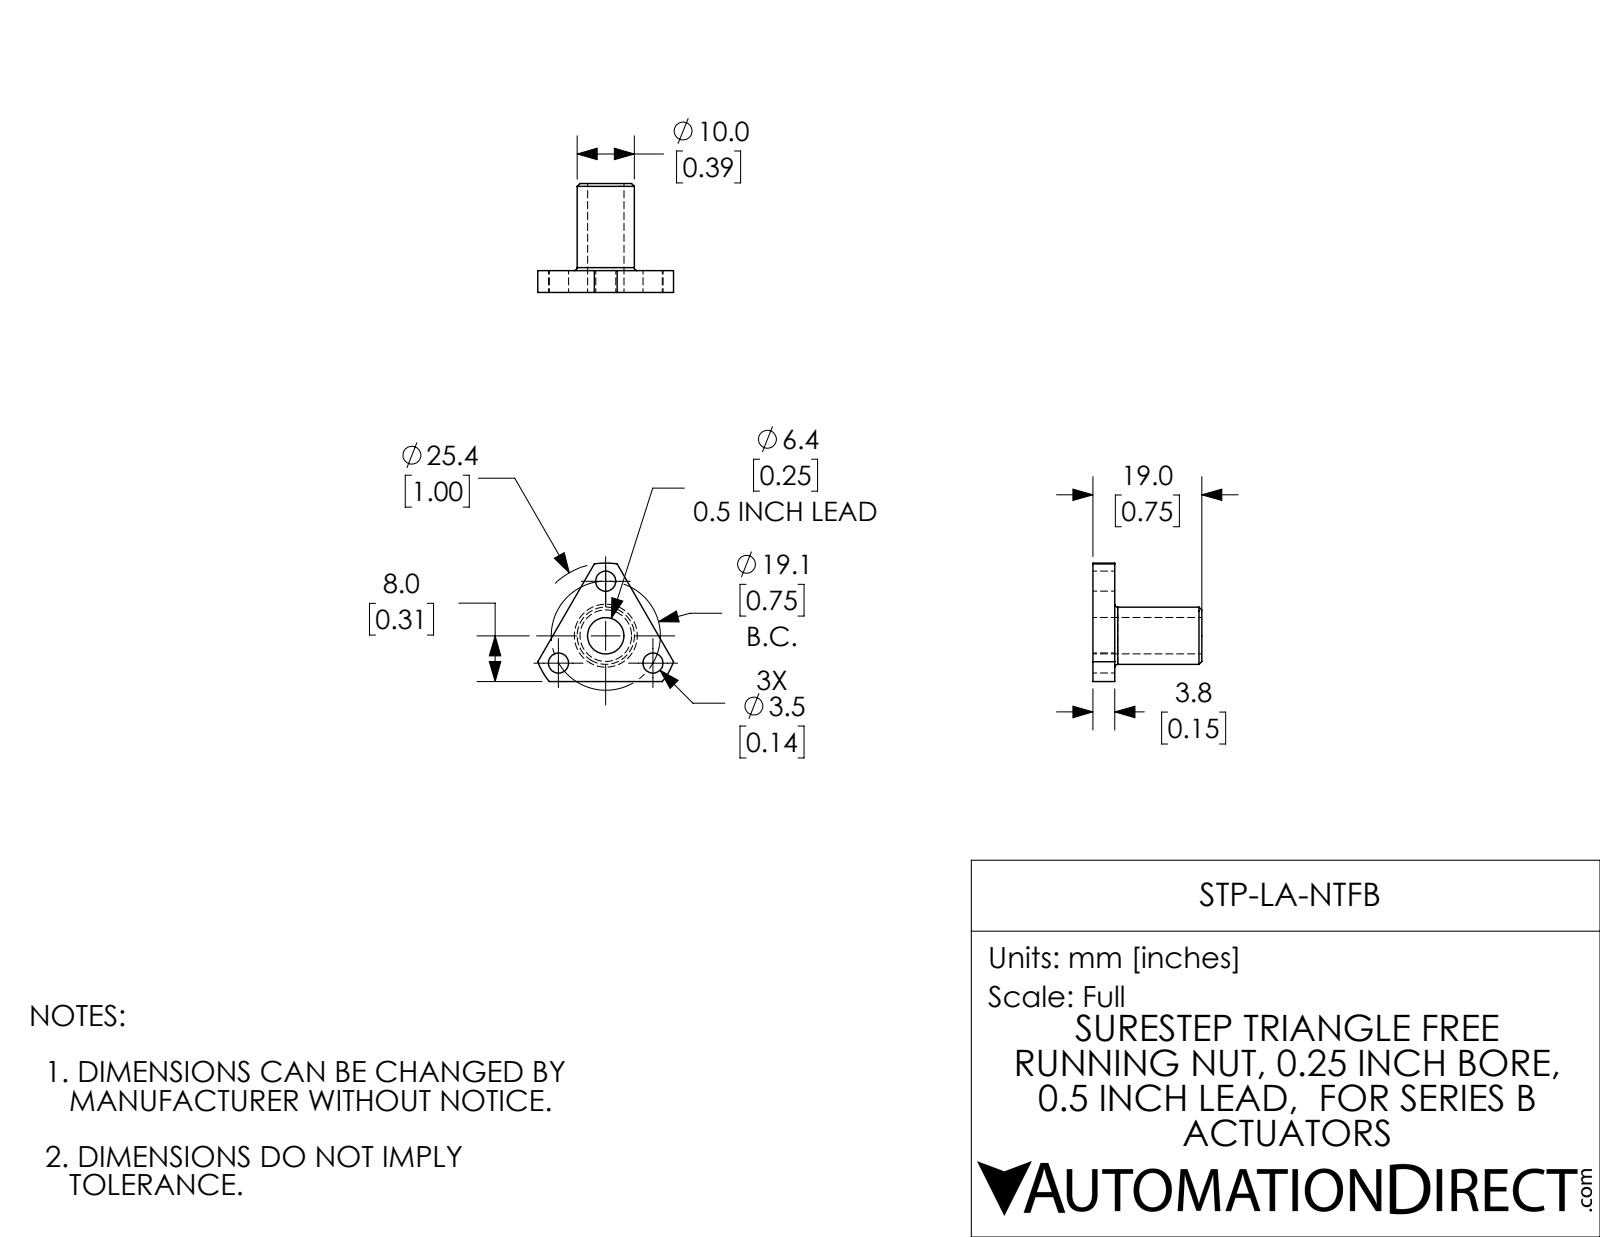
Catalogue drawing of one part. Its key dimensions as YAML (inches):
part_name: "STP-LA-NTFB"
step_written_by: "SolidWorks 2017 (AUTOMOTIVE_DESIGN)"
units: inches
bodies: {solids: 1, faces: 23, planar: 6, cylindrical: 13, other: 4}
overall_size: [0.934, 0.815, 0.748]
volume: 0.102
surface_area: 2.7
round_holes:
  - {diameter: 0.138, count: 3}
  - {diameter: 0.25, count: 1}
round_bosses_or_shafts:
  - {diameter: 0.394, count: 1}
partial_cylinders:
  - {radius: 0.5, count: 1}
face_to_face_distances: [0.15, 0.598, 0.748]
hole_center_spacings: [0.375, 0.649, 0.65]
